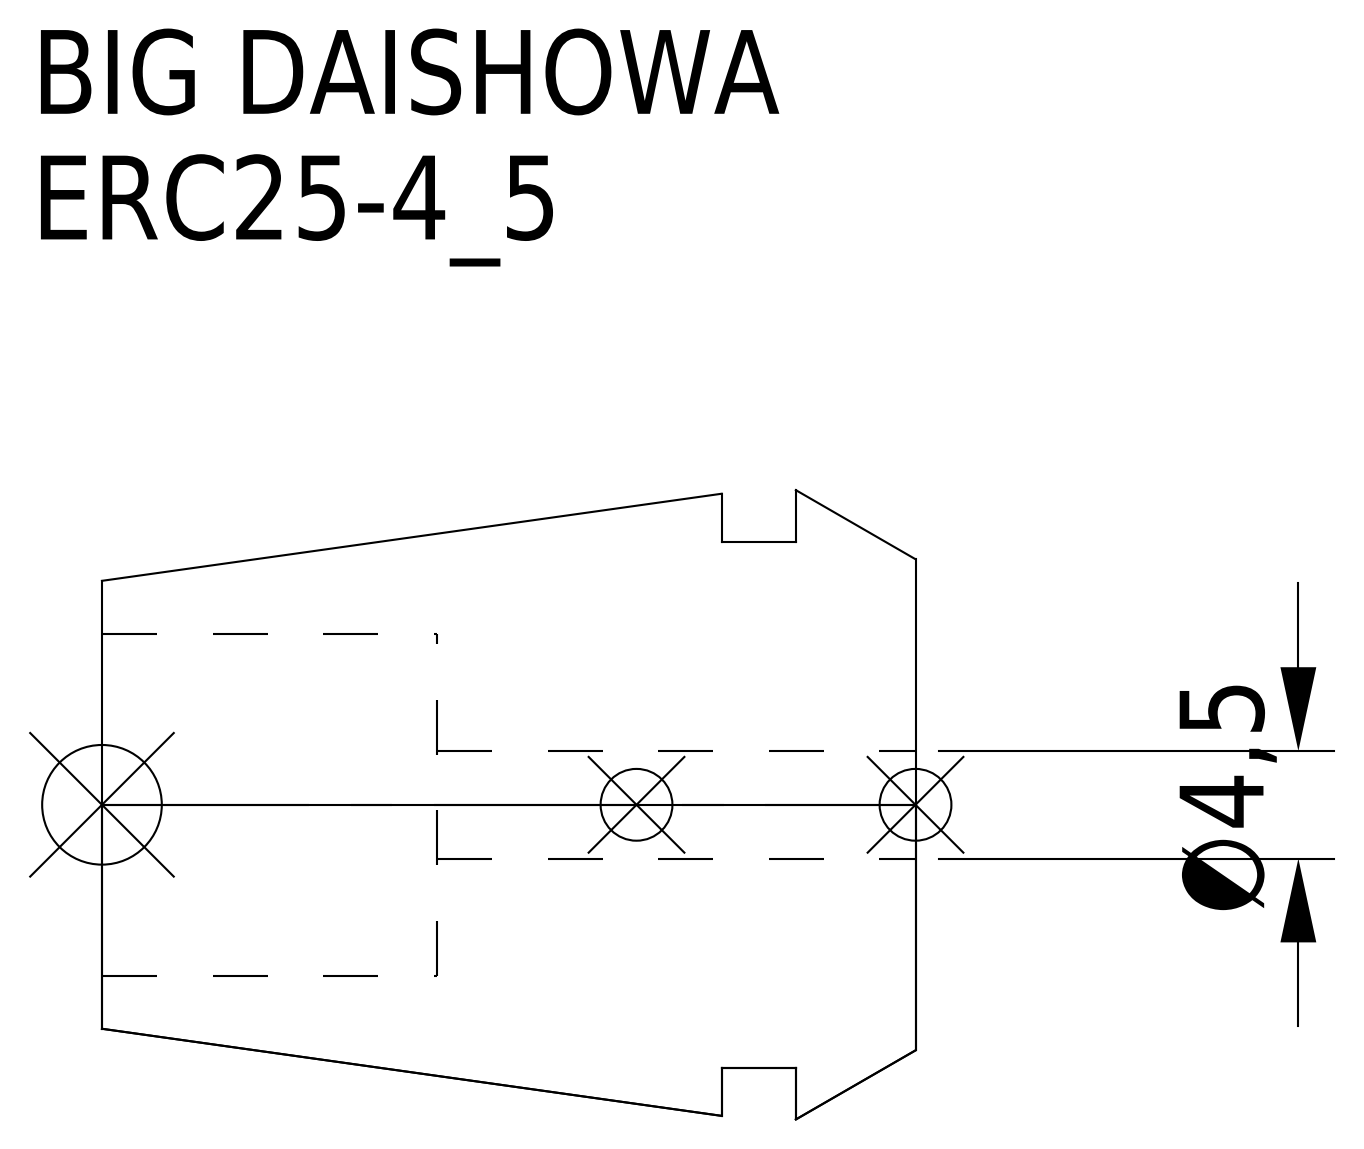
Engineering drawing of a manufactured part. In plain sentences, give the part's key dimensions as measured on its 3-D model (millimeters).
The part is named "ERC25-4_5". Its 3-D file was written by "CREO PARAMETRIC BY PTC INC, 2016380 (AUTOMOTIVE_DESIGN)". It is 1 solid with 15 faces: 5 planar, 6 cylindrical and 4 other. Overall it measures 34 by 26.3 by 26.3 millimeters. Its volume is 11 036 cubic millimeters and its surface area 4 276 square millimeters. Round holes: 1 of diameter 4.5, 1 of diameter 14.3. Round bosses or shafts: 1 of diameter 22. The main face-to-face distances are 5, 8.1, 3.1, 20, 15, 11.9, 34, 29, 25.9, 14.
